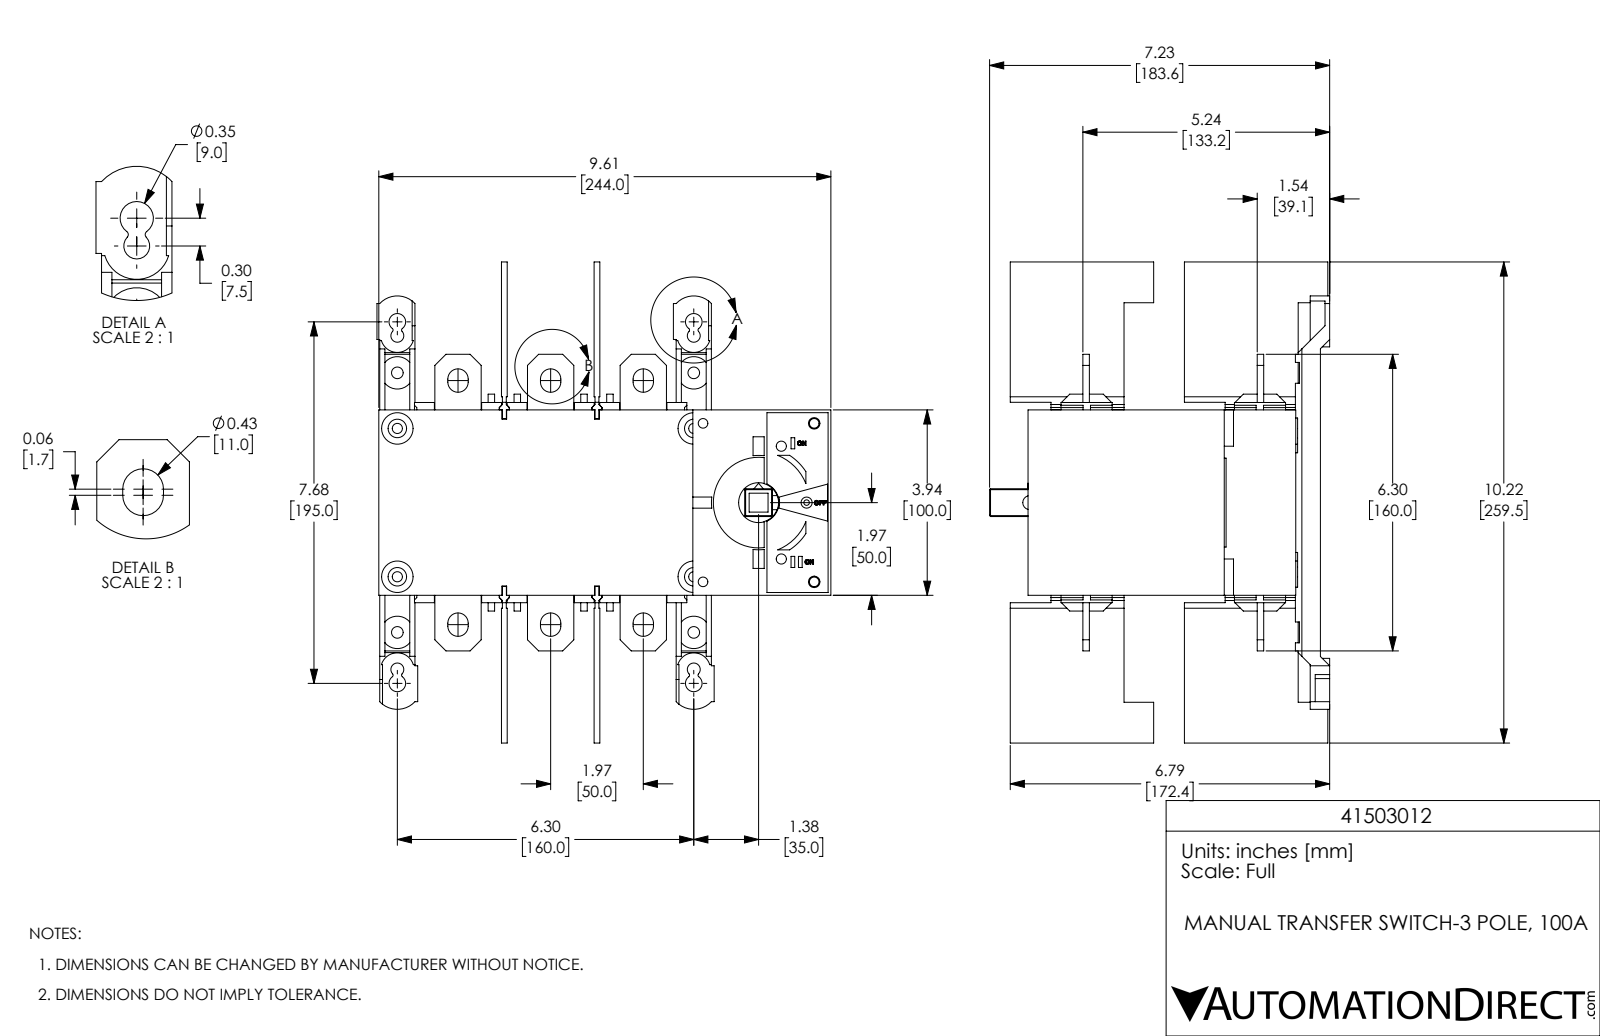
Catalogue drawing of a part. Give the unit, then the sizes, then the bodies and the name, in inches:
Units: inches
Overall size (bounding box): 10.217 × 9.646 × 7.226
Round holes (diameter × count): ⌀0.248 ×12, ⌀0.217 ×6, ⌀0.205 ×4, ⌀0.354 ×4, ⌀0.394 ×4, ⌀0.472 ×4, ⌀0.118 ×1, ⌀0.598 ×1
Round bosses / shafts (diameter × count): ⌀0.669 ×4, ⌀0.848 ×1, ⌀0.591 ×1, ⌀0.236 ×1
Partial cylindrical surfaces — rounded edges, fillets, slot ends (radius × count): R0.217 ×20, R0.344 ×12, R0.039 ×8, R0.049 ×4, R0.059 ×4, R0.138 ×4, R0.236 ×4, R0.354 ×4
Main face-to-face distances: 1.969, 0.122, 3.937, 2.091, 1.846, 5.205, 2.728, 4.909, 2.606, 4.575
Hole centre spacings: 6.299, 2.559, 6.799, 1.083, 1.476, 2.056, 4.035, 5.118
Volume: 180.4 in³ · Surface area: 550.3 in²
Bodies: 11 solids, 1386 faces (1134 planar, 248 cylindrical, 4 other)
Part name (STEP PRODUCT): 41503012
STEP written by: SolidWorks 2017 (AUTOMOTIVE_DESIGN)
